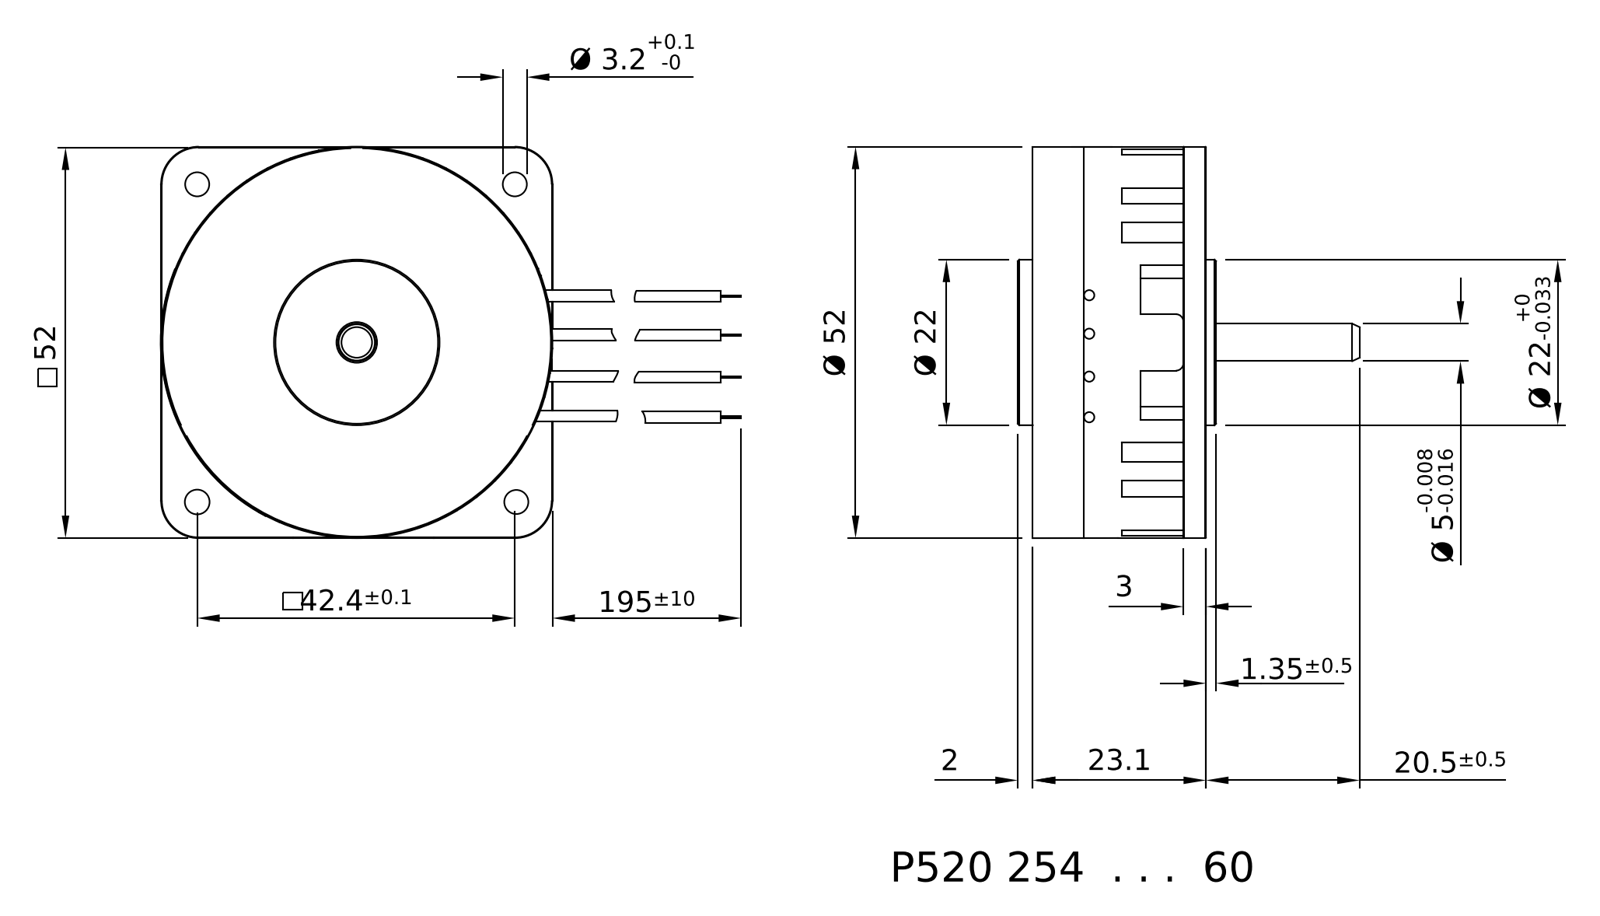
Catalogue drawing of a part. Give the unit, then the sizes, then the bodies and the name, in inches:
Units: inches
Overall size (bounding box): 2.831 × 2.047 × 1.795
Round holes (diameter × count): ⌀0.126 ×7, ⌀0.078 ×6, ⌀0.079 ×6, ⌀0.087 ×4, ⌀0.122 ×3, ⌀0.151 ×3, ⌀0.213 ×1
Round bosses / shafts (diameter × count): ⌀0.06 ×4, ⌀0.031 ×4, ⌀0.213 ×3, ⌀0.089 ×3, ⌀2.047 ×1, ⌀0.866 ×1, ⌀0.197 ×1
Partial cylindrical surfaces — rounded edges, fillets, slot ends (radius × count): R0.004 ×8, R0.197 ×4, R0.11 ×3, R0.833 ×1, R0.844 ×1, R0.866 ×1
Main face-to-face distances: 0.521, 0.118, 0.639, 0.27, 0.791, 0.909, 0.13, 0.349, 0.079, 0.87
Hole centre spacings: 0.921, 0.458, 0.904, 1.18, 1.669, 1.642, 0.189, 0.325
Volume: 3.048 in³ · Surface area: 33.65 in²
Bodies: 15 solids, 385 faces (164 planar, 161 cylindrical, 60 other)
Part name (STEP PRODUCT): 2-800-50-0327_1; 2-420-50-0006-Z_ASM_1_ASM; 2-800-50-0039_1; 2-800-50-0320-05_1 (+6 more)
STEP written by: PRO/ENGINEER BY PARAMETRIC TECHNOLOGY CORPORATION, 2014310 (CONFIG_CONTROL_DESIGN)
